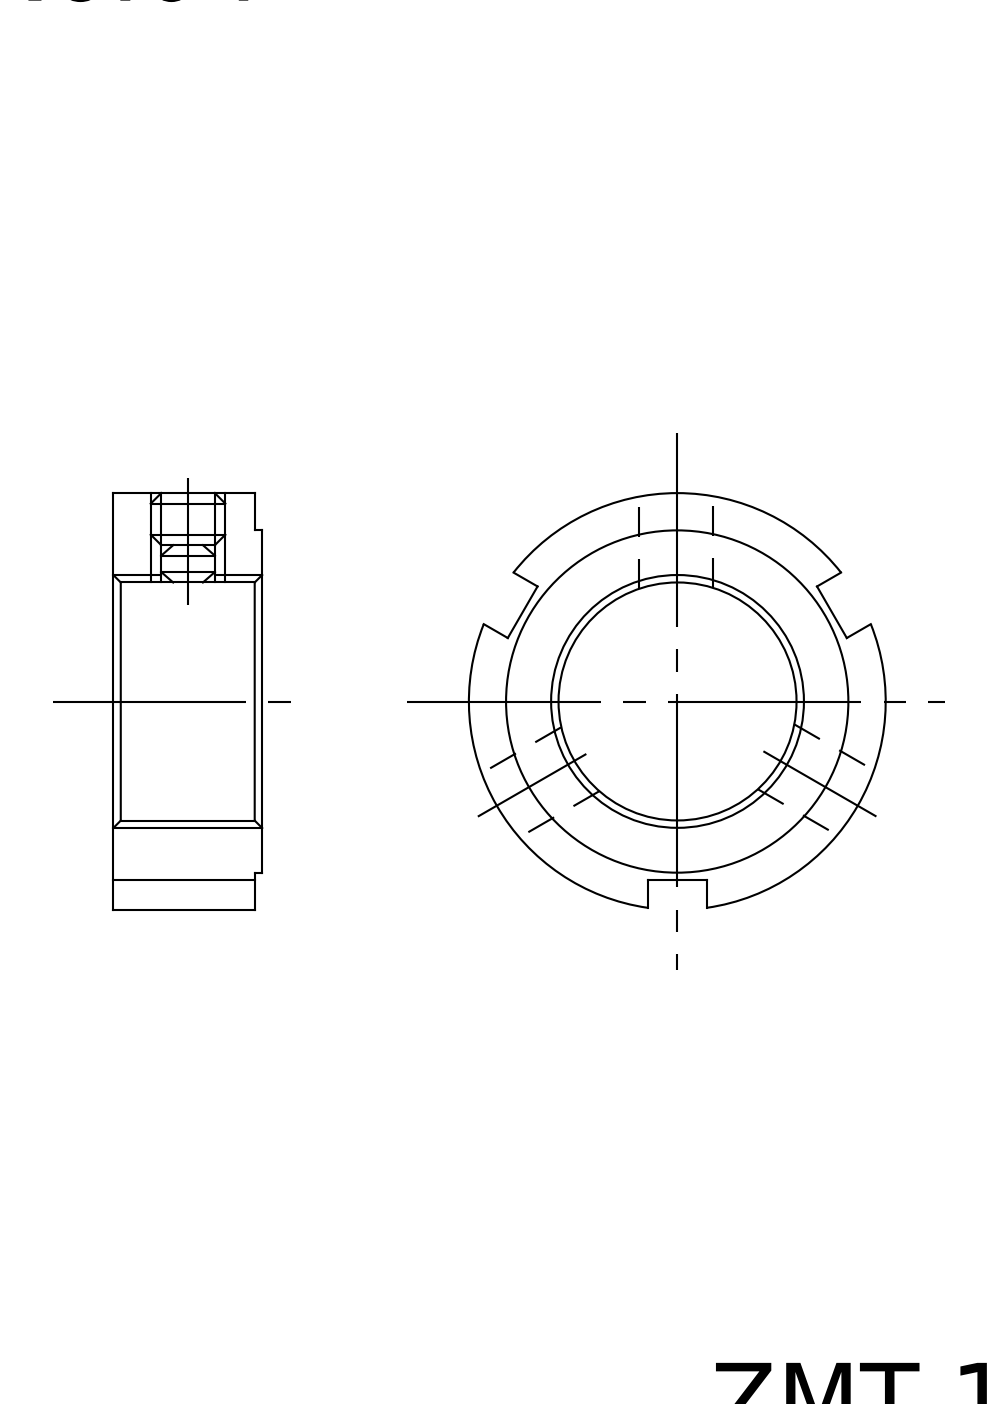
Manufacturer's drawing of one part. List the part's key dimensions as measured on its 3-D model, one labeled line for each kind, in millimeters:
Part name (STEP PRODUCT): FKD ZMT 17
STEP written by: Autodesk Inventor 2011 (AUTOMOTIVE_DESIGN)
Units: millimetres
Bodies: 1 solid, 20 faces (12 planar, 8 cylindrical, 0 other)
Overall size (bounding box): 28 × 27.86 × 10
Volume: 3 343 mm³ · Surface area: 2 377 mm²
Round holes (diameter × count): ⌀4.13 ×3, ⌀17 ×1
Round bosses / shafts (diameter × count): ⌀28 ×1, ⌀23 ×1
Main face-to-face distances: 10, 0.5, 9.5, 4
